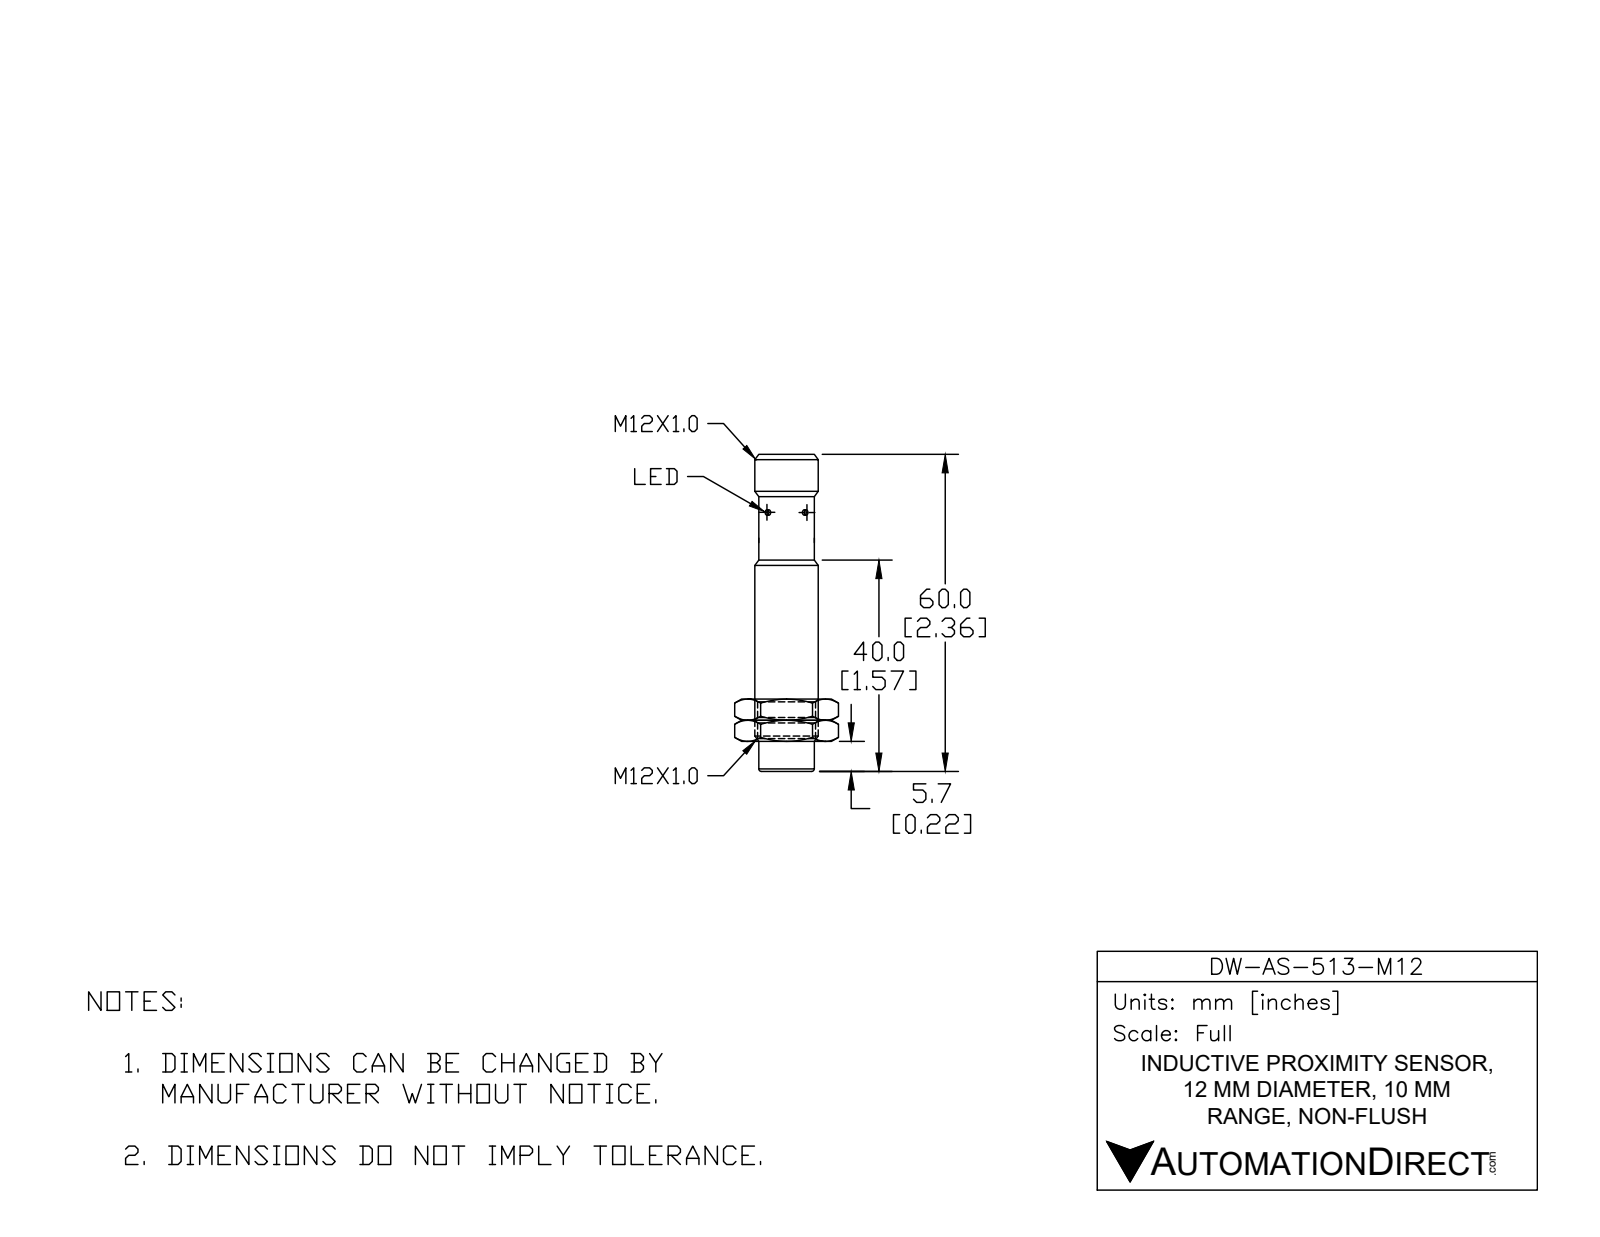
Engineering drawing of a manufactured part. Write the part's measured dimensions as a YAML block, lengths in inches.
part_name: "DW-AS-513-M12"
step_written_by: "SolidWorks 2017 (AUTOMOTIVE_DESIGN)"
units: inches
bodies: {solids: 1, faces: 52, planar: 13, cylindrical: 28, other: 11}
overall_size: [2.362, 0.472, 0.472]
volume: 0.351
surface_area: 4.488
round_holes:
  - {diameter: 0.118, count: 2}
  - {diameter: 0.335, count: 1}
round_bosses_or_shafts:
  - {diameter: 0.04, count: 4}
  - {diameter: 0.472, count: 1}
  - {diameter: 0.421, count: 1}
  - {diameter: 0.415, count: 1}
partial_cylinders:
  - {radius: 0.019, count: 1}
  - {radius: 0.02, count: 1}
  - {radius: 0.193, count: 1}
  - {radius: 0.206, count: 1}
face_to_face_distances: [2.02, 2.362, 0.343, 0.039, 1.614, 0.406, 0.748, 2.047, 0.433, 0.028]
